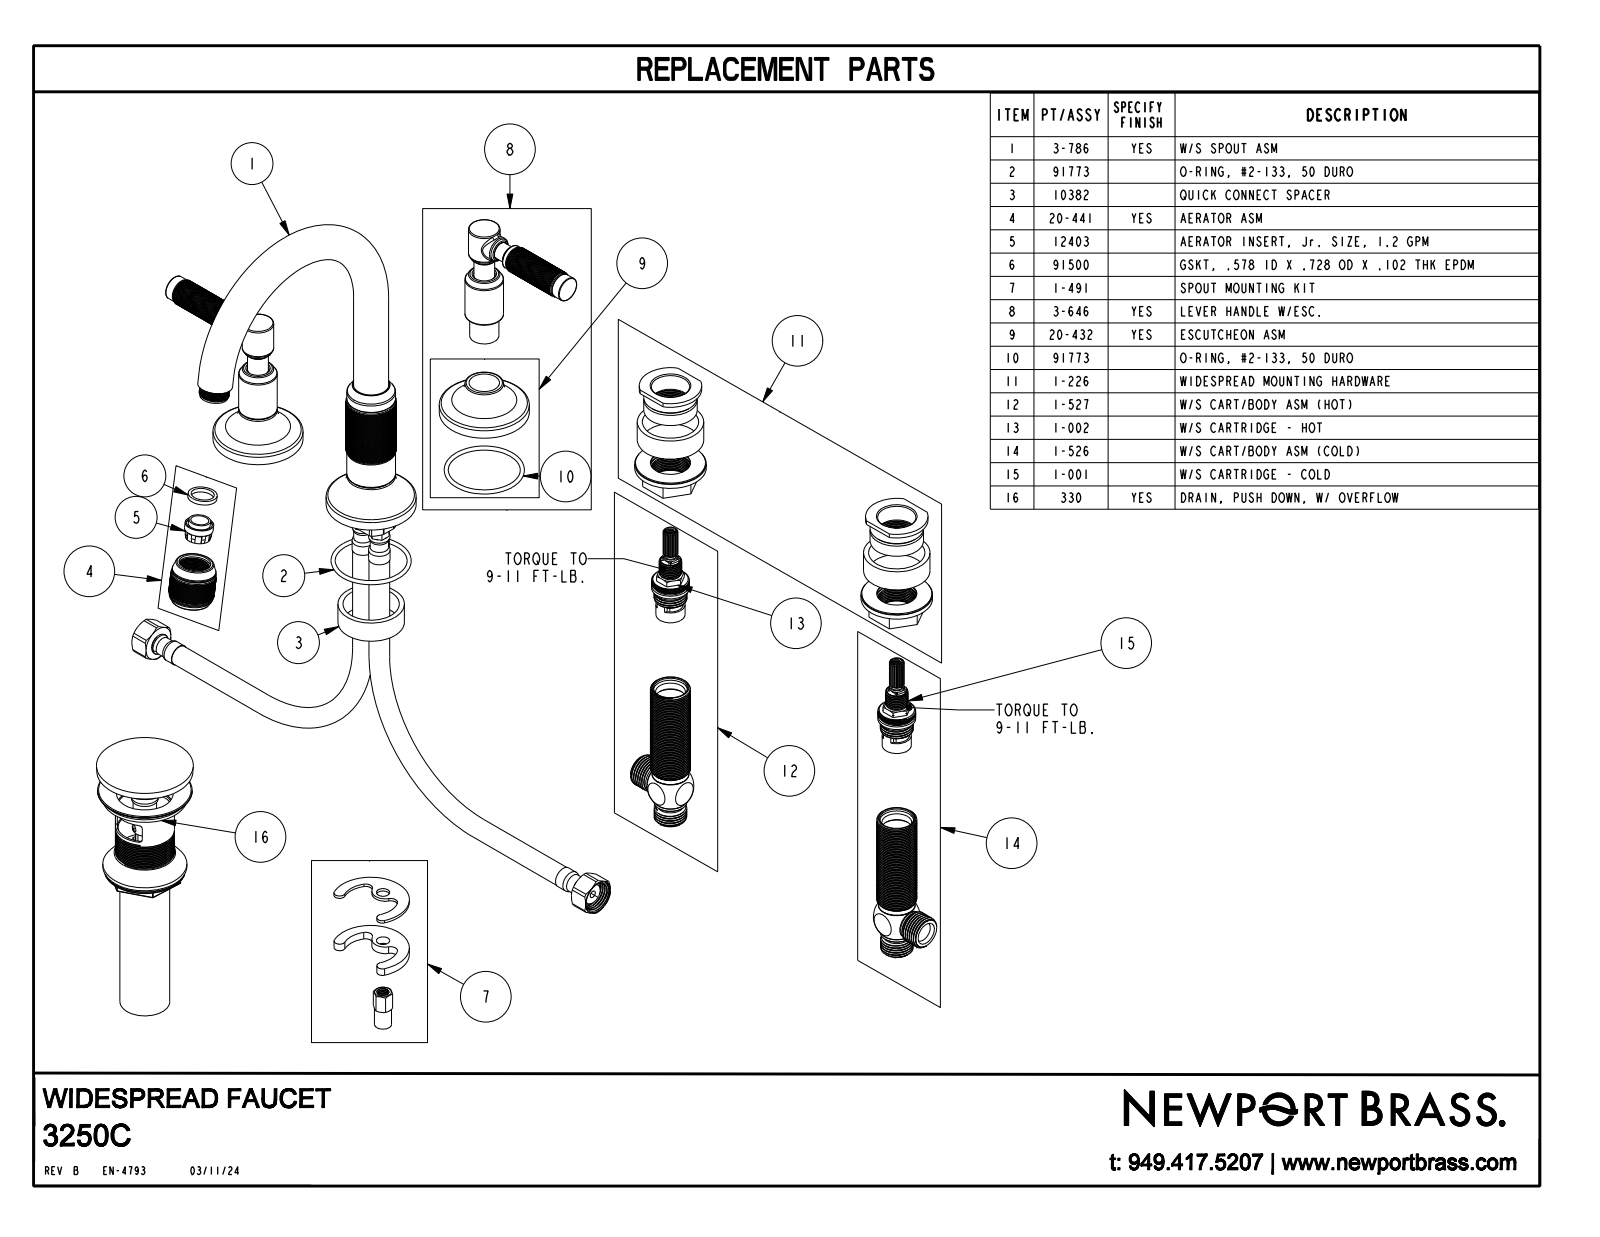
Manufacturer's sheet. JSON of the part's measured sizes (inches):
{"part_name": "3250C", "step_written_by": "CREO PARAMETRIC BY PTC INC, 2023134 (CONFIG_CONTROL_DESIGN)", "units": "inches", "bodies": {"solids": 3, "faces": 24298, "planar": 132, "cylindrical": 4788, "other": 19378}, "overall_size": [14.062, 9.504, 7.324], "volume_in3": 21.28, "surface_area_in2": 119.7, "round_holes": [[0.11, 2], [0.36, 2], [0.56, 2], [0.403, 1], [0.47, 1], [0.62, 1], [0.691, 1], [0.881, 1]], "round_bosses_or_shafts": [[2.25, 3], [0.965, 2], [0.875, 2], [0.85, 2], [0.787, 2], [0.52, 2], [1.26, 1], [1.22, 1]], "partial_cylinders_radius": [[0.137, 2], [0.34, 1]], "face_to_face_distances": [2.158, 0.325, 0.55, 0.225, 0.9, 1.258, 0.91, 1.248, 2.299, 1.399], "hole_center_spacings": [4, 8]}
